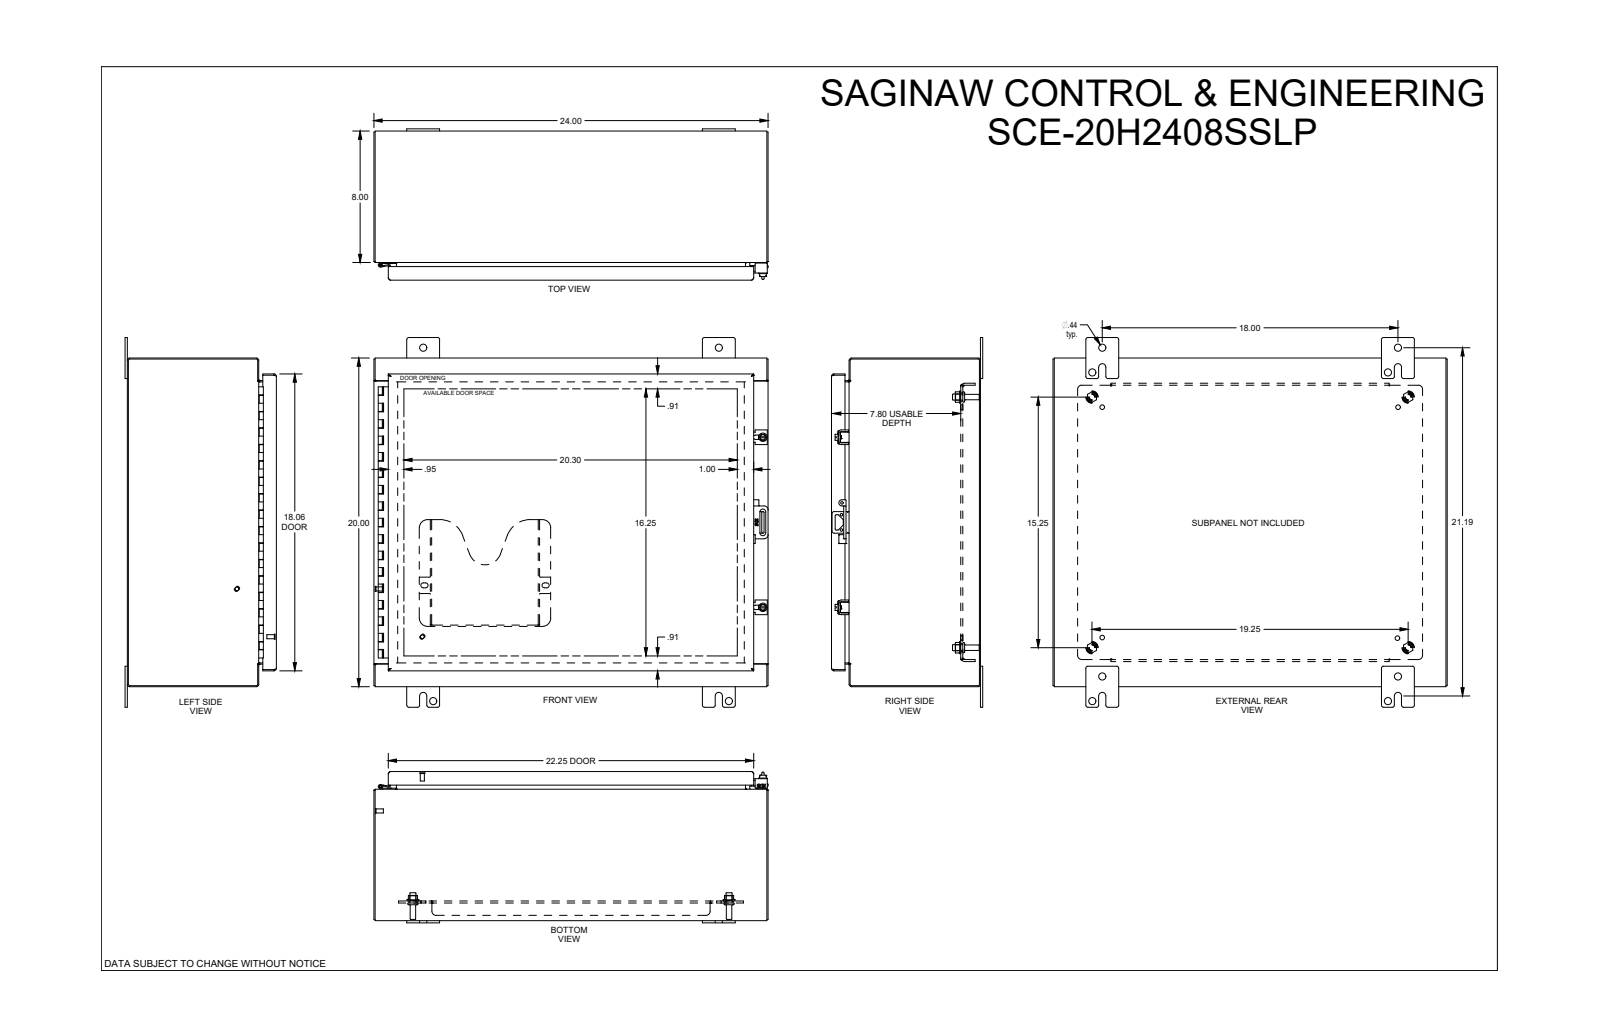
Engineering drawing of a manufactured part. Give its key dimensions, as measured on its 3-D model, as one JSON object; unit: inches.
{"part_name": "SCE-20H2408SSLP", "step_written_by": "SolidWorks 2019 (CONFIG_CONTROL_DESIGN)", "units": "inches", "bodies": {"solids": 0, "faces": 3049, "planar": 1222, "cylindrical": 632, "other": 1195}, "overall_size": [24, 22.5, 9.208], "round_holes": [[0.437, 8], [0.25, 5], [0.281, 4], [0.367, 4], [0.5, 4], [0.19, 3], [0.193, 3], [0.16, 2], [0.203, 2], [0.13, 1], [0.132, 1]], "round_bosses_or_shafts": [[0.248, 7], [0.563, 5], [0.366, 4], [0.332, 4], [0.256, 3], [0.25, 3], [0.188, 3], [0.507, 2]], "partial_cylinders_radius": [[0.01, 108], [0.015, 36], [0.029, 30], [0.03, 27], [0.125, 27], [0.06, 25], [0.04, 22], [0.07, 14]], "face_to_face_distances": [0.075, 8.998, 8.923, 0.075, 8.998, 9.073, 19.925, 7.923, 1.2, 1.125], "hole_center_spacings": [0.875, 18, 26.907, 14.644, 18.641, 23.689, 0.516, 1.439]}
